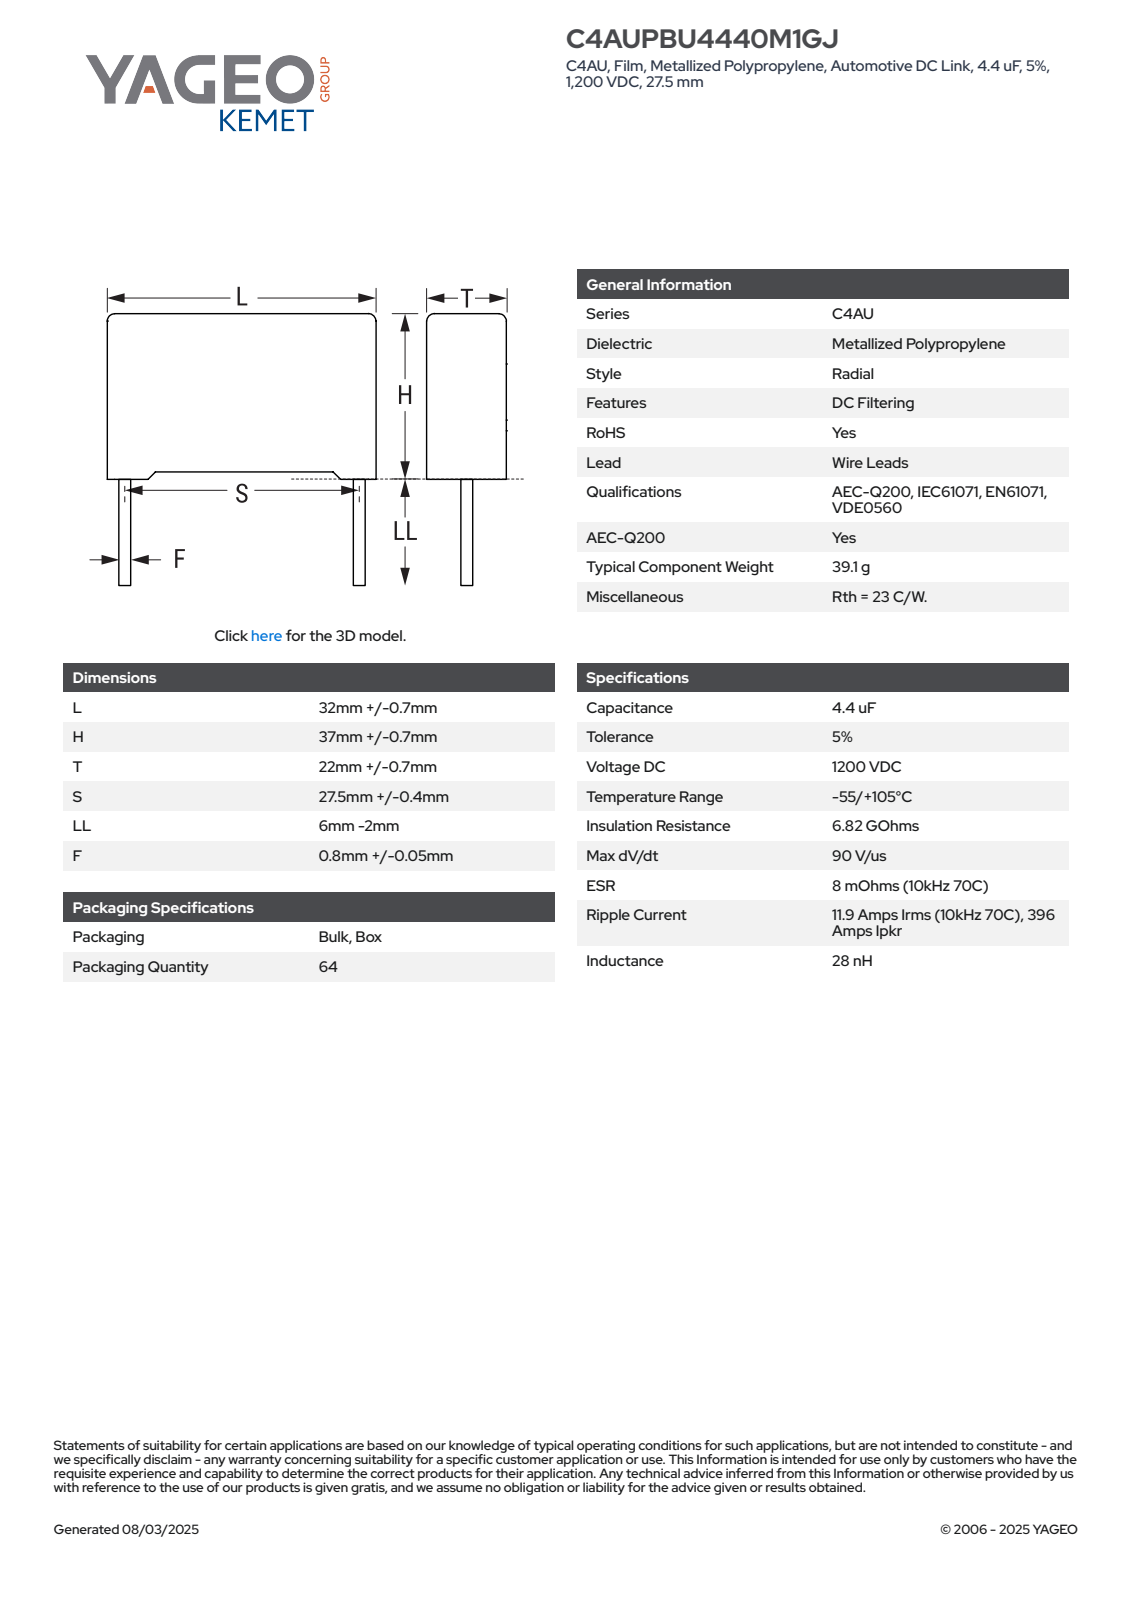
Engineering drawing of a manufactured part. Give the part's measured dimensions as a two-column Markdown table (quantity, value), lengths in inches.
| quantity | value |
| --- | --- |
| part name | CFR_RB2CFP_32X37X22_L32.7H37.7T22.7S27.5LL4F0.85 |
| STEP written by | SolidWorks 2014 (AUTOMOTIVE_DESIGN) |
| units | inches |
| bodies | 4 solids, 85 faces (77 planar, 8 cylindrical, 0 other) |
| overall size | 1.642 × 1.287 × 0.894 |
| volume | 1.659 in³ |
| surface area | 8.892 in² |
| round bosses / shafts (diameter × count) | 0.033 × 2 |
| partial cylindrical surfaces (radius × count) | 0.02 × 4 |
| main face-to-face distances | 0.894, 1.287, 1.433, 0.022, 1.455, 0.03, 0.051, 1.484, 0.043, 1.244 |
